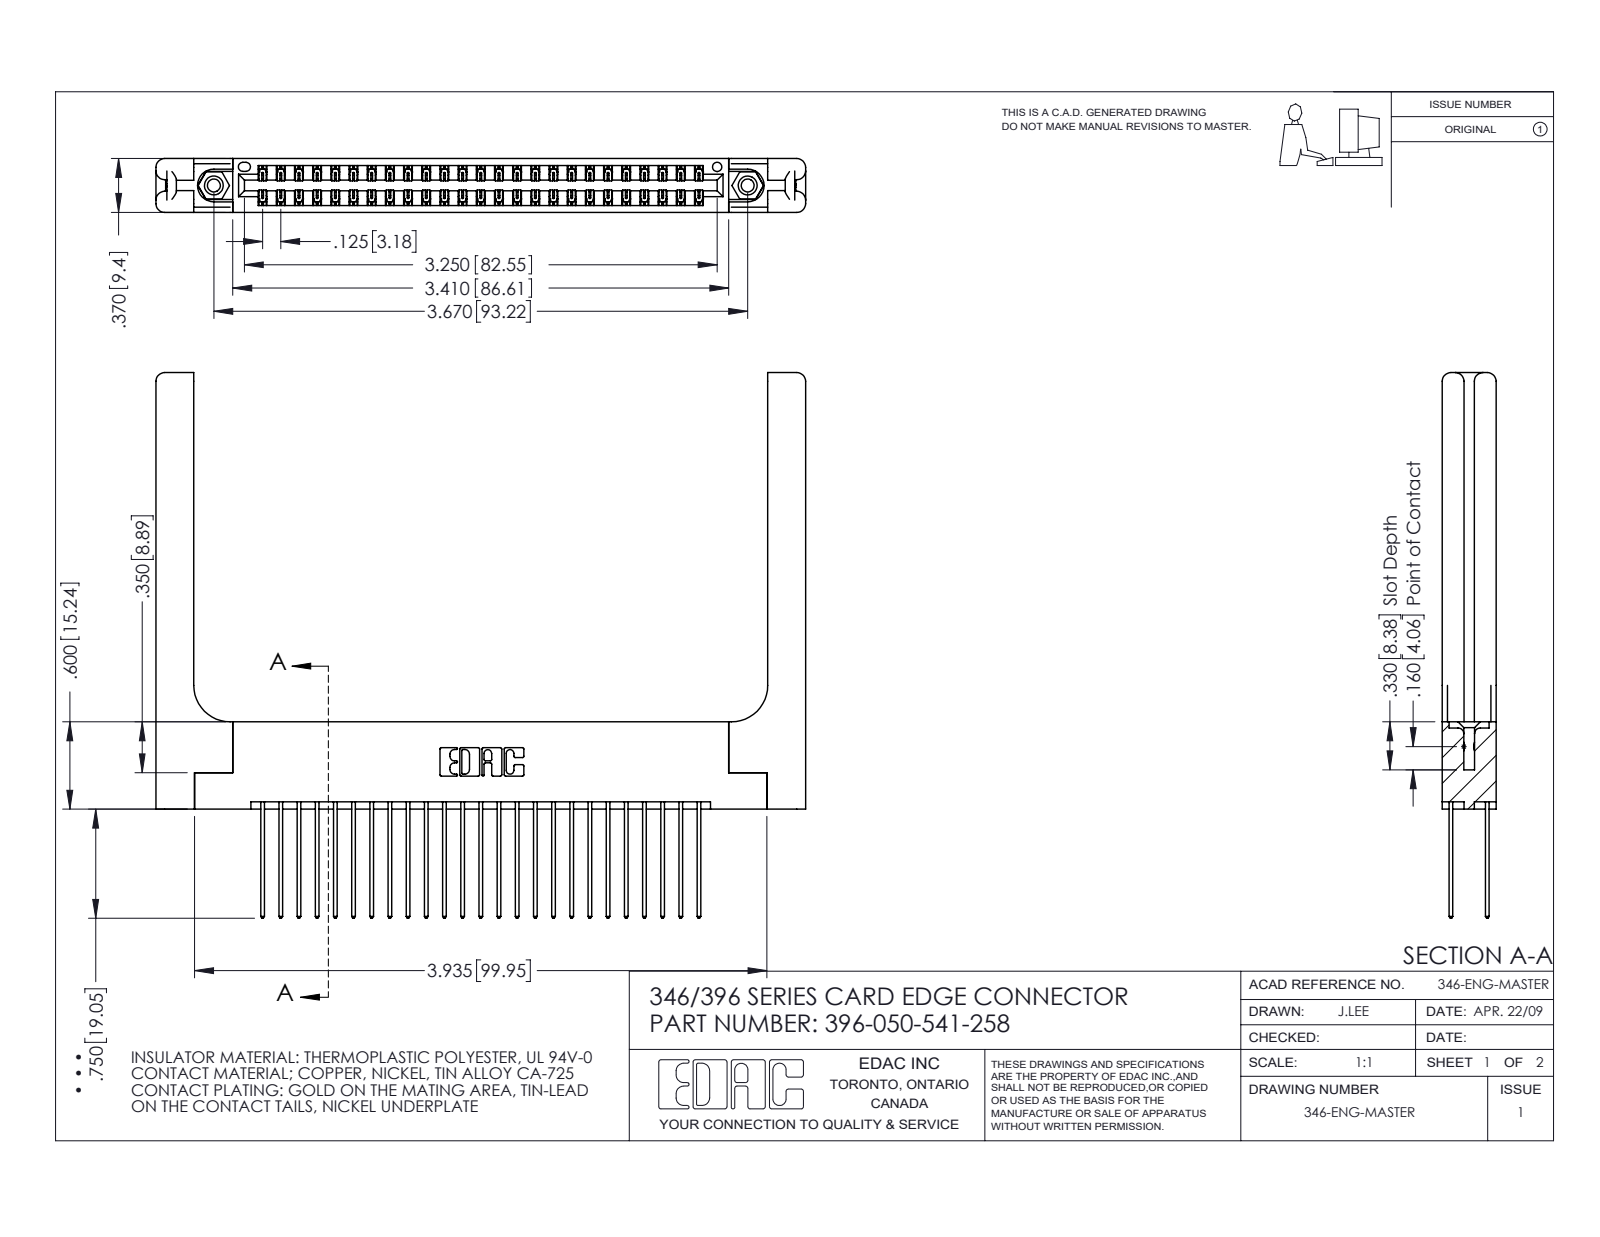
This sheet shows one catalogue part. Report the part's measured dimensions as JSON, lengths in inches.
{"part_name": "345-250-001_345-250-001-102; 345-292-001_345-293-141; 346 Part_Flush Mounting Lugs - 0.156 Dia-TH; 346-220-058_345-220-058 (+1 more)", "step_written_by": "SolidWorks 2016 (CONFIG_CONTROL_DESIGN)", "units": "inches", "bodies": {"solids": 55, "faces": 2978, "planar": 1974, "cylindrical": 944, "other": 60}, "overall_size": [4.466, 3.75, 0.37], "volume_in3": 1.142, "surface_area_in2": 33.32, "round_holes": [[0.089, 2], [0.125, 2], [0.156, 2], [0.064, 1]], "round_bosses_or_shafts": [[0.155, 2]], "partial_cylinders_radius": [[0.006, 75], [0.01, 50], [0.01, 22], [0.06, 16], [0.007, 6], [0.031, 6], [0.026, 3], [0.014, 2]], "face_to_face_distances": [0.072, 0.048, 0.322, 0.37, 0.25, 0.025, 0.298, 0.148, 0.15, 0.275], "hole_center_spacings": [0.246, 3.462, 3.67]}
